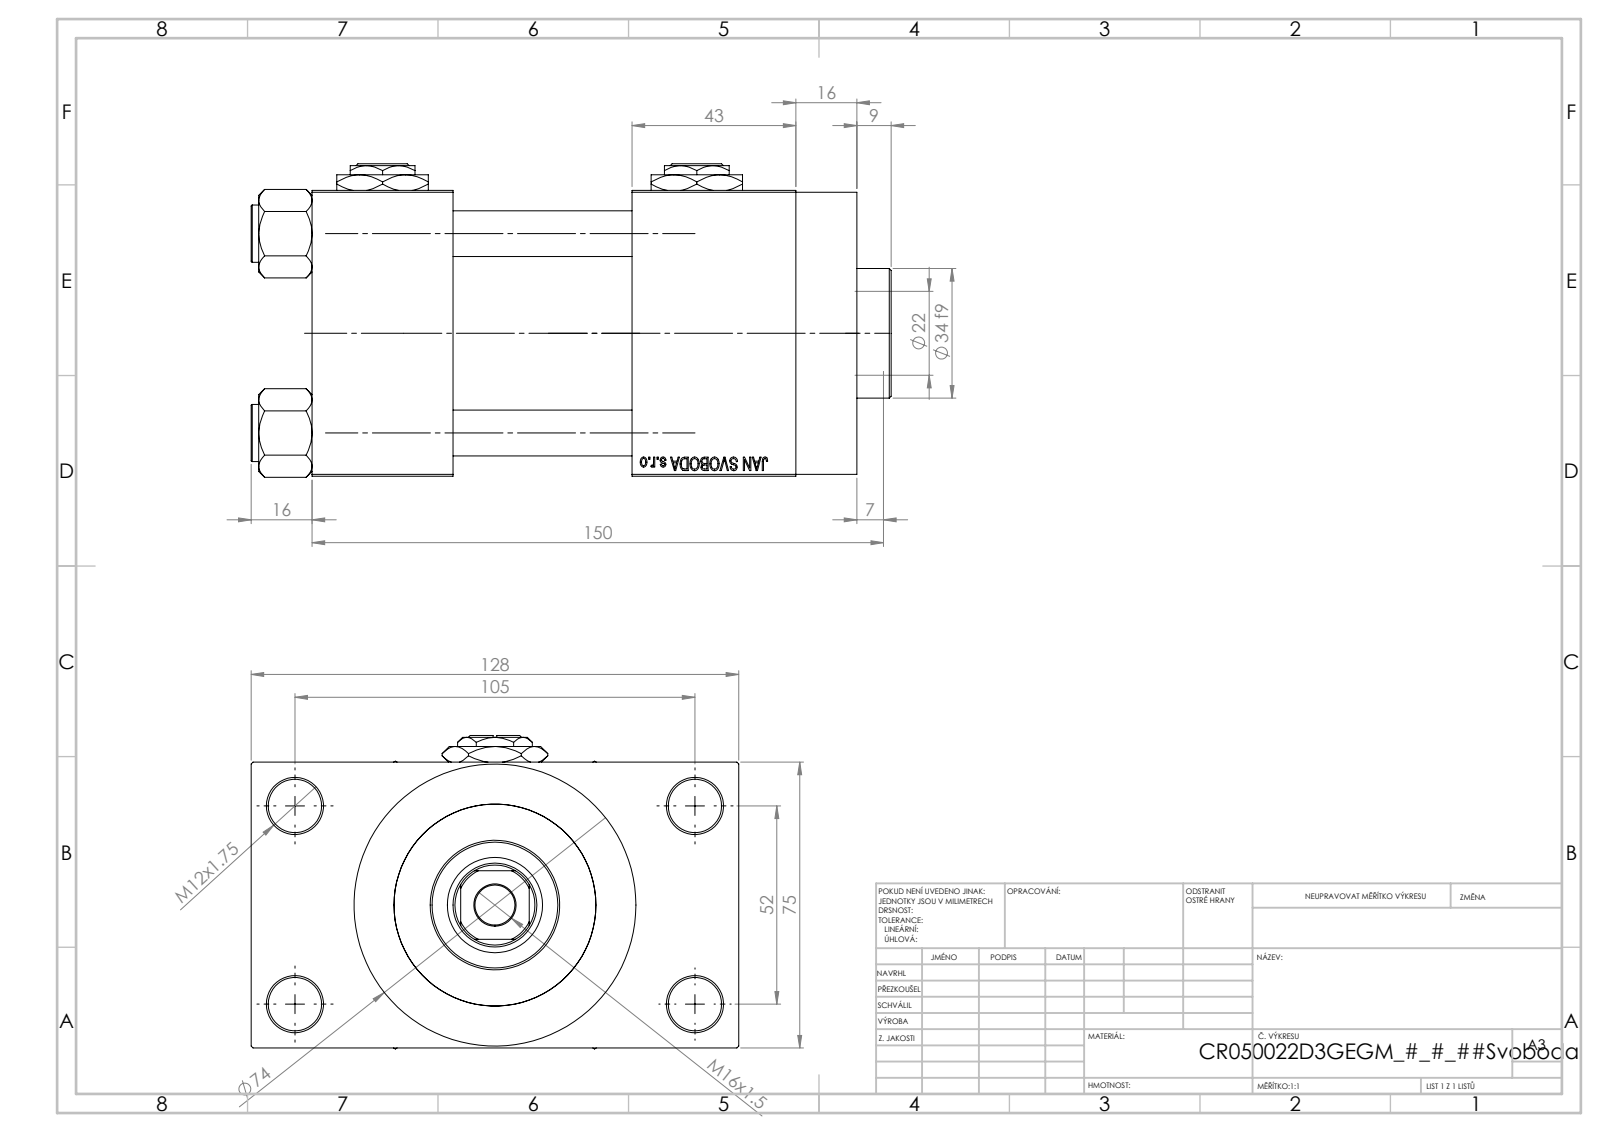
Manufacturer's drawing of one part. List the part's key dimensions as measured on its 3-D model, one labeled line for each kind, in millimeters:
Part name (STEP PRODUCT): V215CR_D_Body; Zatka_pro_OIL_PORT; V215_VC_A; V215CR_VCP_D (+2 more)
STEP written by: SolidWorks 2019 (CONFIG_CONTROL_DESIGN)
Units: millimetres
Bodies: 13 solids, 1205 faces (545 planar, 100 cylindrical, 560 other)
Overall size (bounding box): 168 × 128 × 82.27
Volume: 753 765 mm³ · Surface area: 158 326 mm²
Round holes (diameter × count): ⌀12 ×4, ⌀14 ×4, ⌀7 ×2, ⌀20.96 ×2, ⌀30 ×2, ⌀10.5 ×1, ⌀22 ×1, ⌀25 ×1, ⌀41 ×1, ⌀50 ×1, ⌀53 ×1
Round bosses / shafts (diameter × count): ⌀15 ×4, ⌀74 ×1, ⌀56 ×1, ⌀34 ×1
Partial cylindrical surfaces — rounded edges, fillets, slot ends (radius × count): R10.5 ×1
Main face-to-face distances: 75, 47, 37, 84, 26.5, 101.5, 43, 127, 90, 59
Hole centre spacings: 26.35, 36.98, 52.3, 58.43, 58.59, 78.65, 94.37, 52
